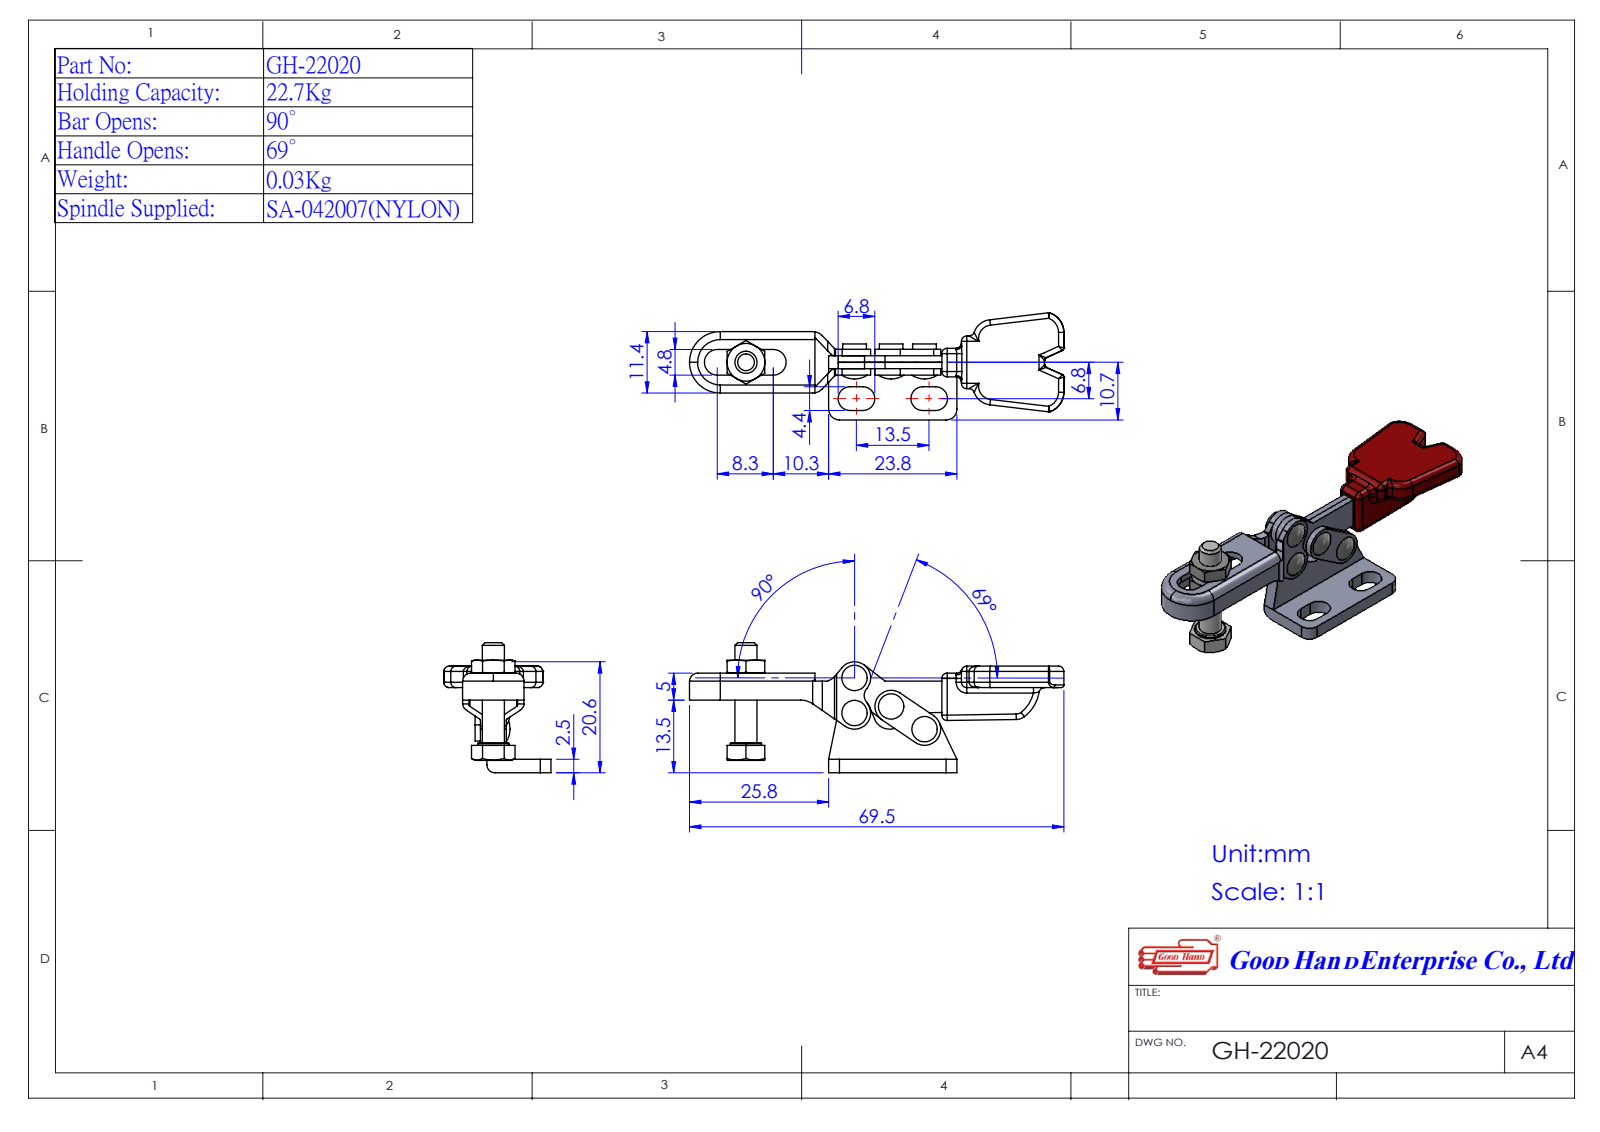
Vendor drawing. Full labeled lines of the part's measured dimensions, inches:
Part name (STEP PRODUCT): 12202013(簡化); GH-22020(簡化); Group5^GH-22020(簡化); Group3^GH-22020(簡化) (+2 more)
STEP written by: SolidWorks 2016 (AUTOMOTIVE_DESIGN)
Units: inches
Bodies: 5 solids, 278 faces (117 planar, 113 cylindrical, 48 other)
Overall size (bounding box): 2.736 × 1.008 × 0.783
Volume: 0.275 in³ · Surface area: 8.189 in²
Round holes (diameter × count): ⌀0.079 ×4
Round bosses / shafts (diameter × count): ⌀0.138 ×4, ⌀0.236 ×1, ⌀0.228 ×1, ⌀0.161 ×1
Partial cylindrical surfaces — rounded edges, fillets, slot ends (radius × count): R0.039 ×20, R0.02 ×5, R0.118 ×5, R0.079 ×4, R0.087 ×4, R0.098 ×3, R0.094 ×2, R0.138 ×2
Main face-to-face distances: 0.047, 0.094, 0.098, 0.681, 0.177, 0.224, 0.272, 0.13, 0.059, 0.106
Hole centre spacings: 0.256, 0.272, 0.295, 0.339, 0.525, 0.634
